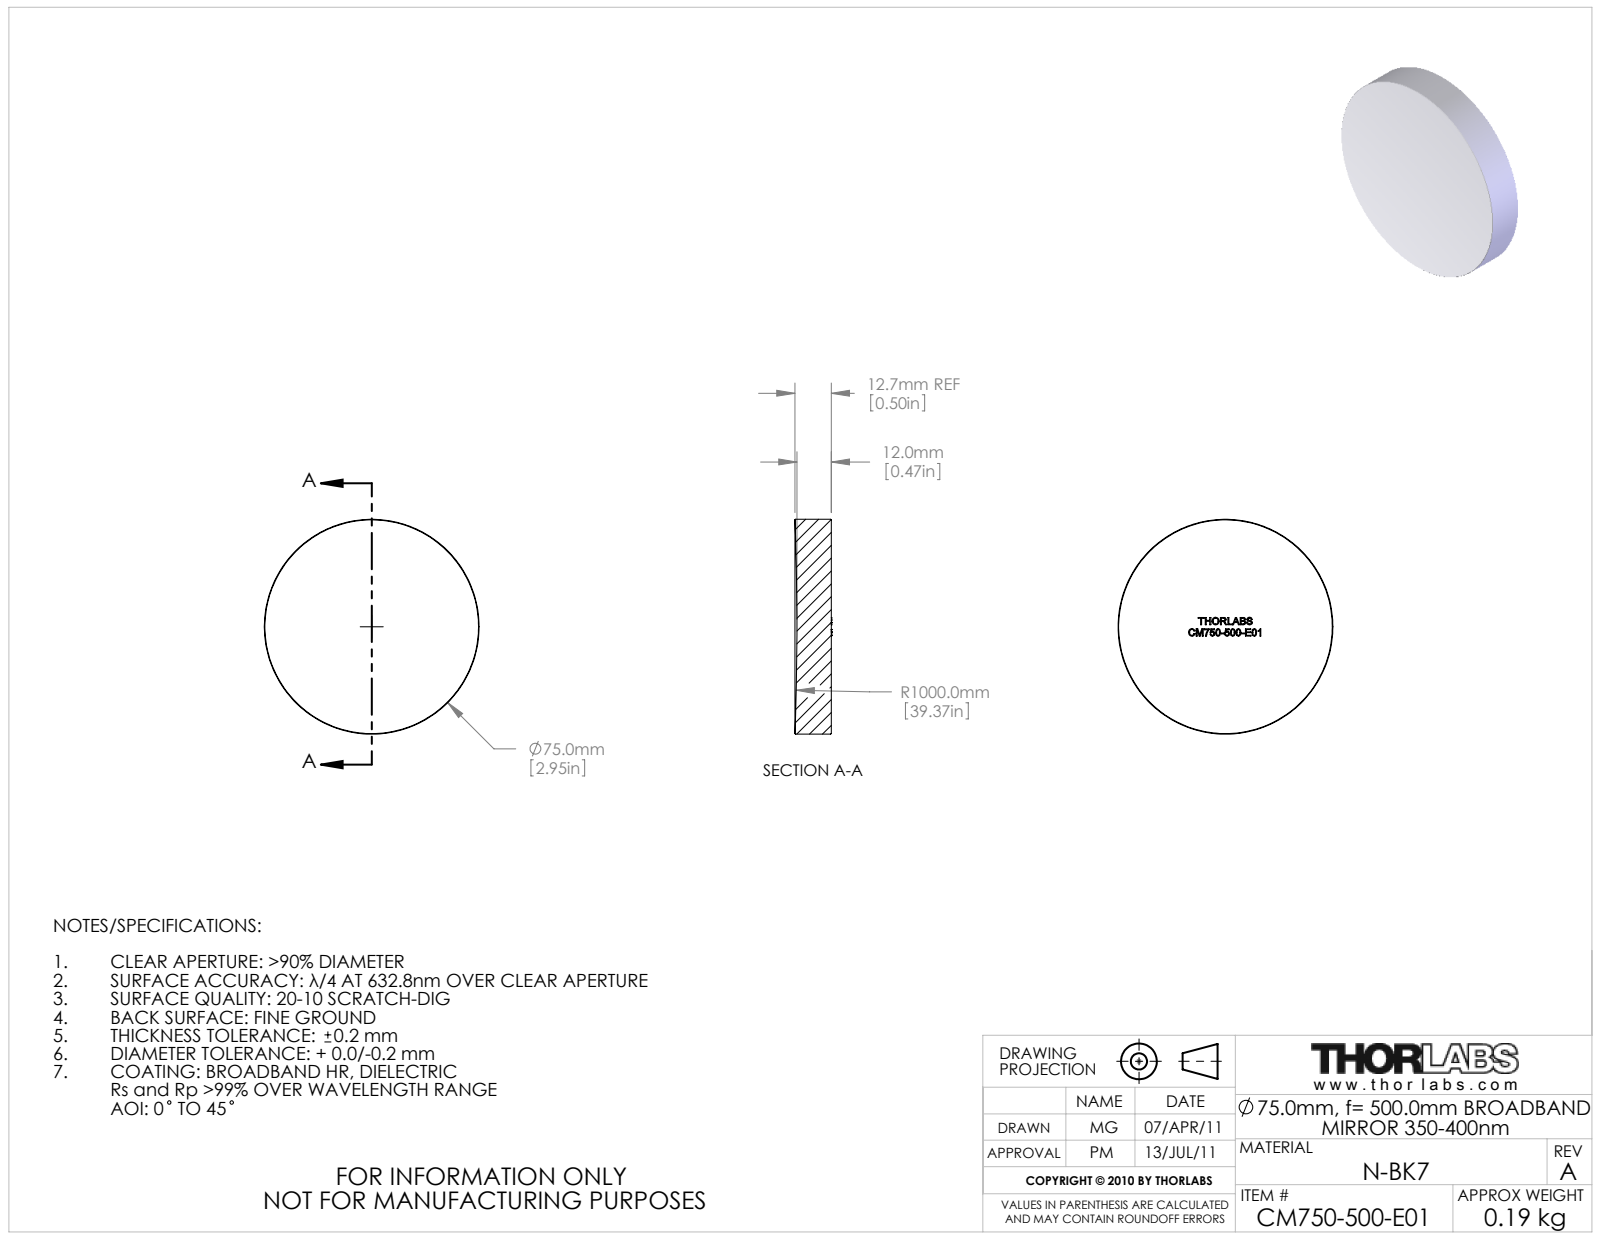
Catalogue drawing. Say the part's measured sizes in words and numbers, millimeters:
The part is named "22622-E0W". Its 3-D file was written by "SolidWorks 2011 (AUTOMOTIVE_DESIGN)". It is 0 solids with 40 faces: 32 planar, 2 cylindrical and 6 other. Overall it measures 75 by 75 by 12.7 millimeters. Round bosses or shafts: 1 of diameter 75.
